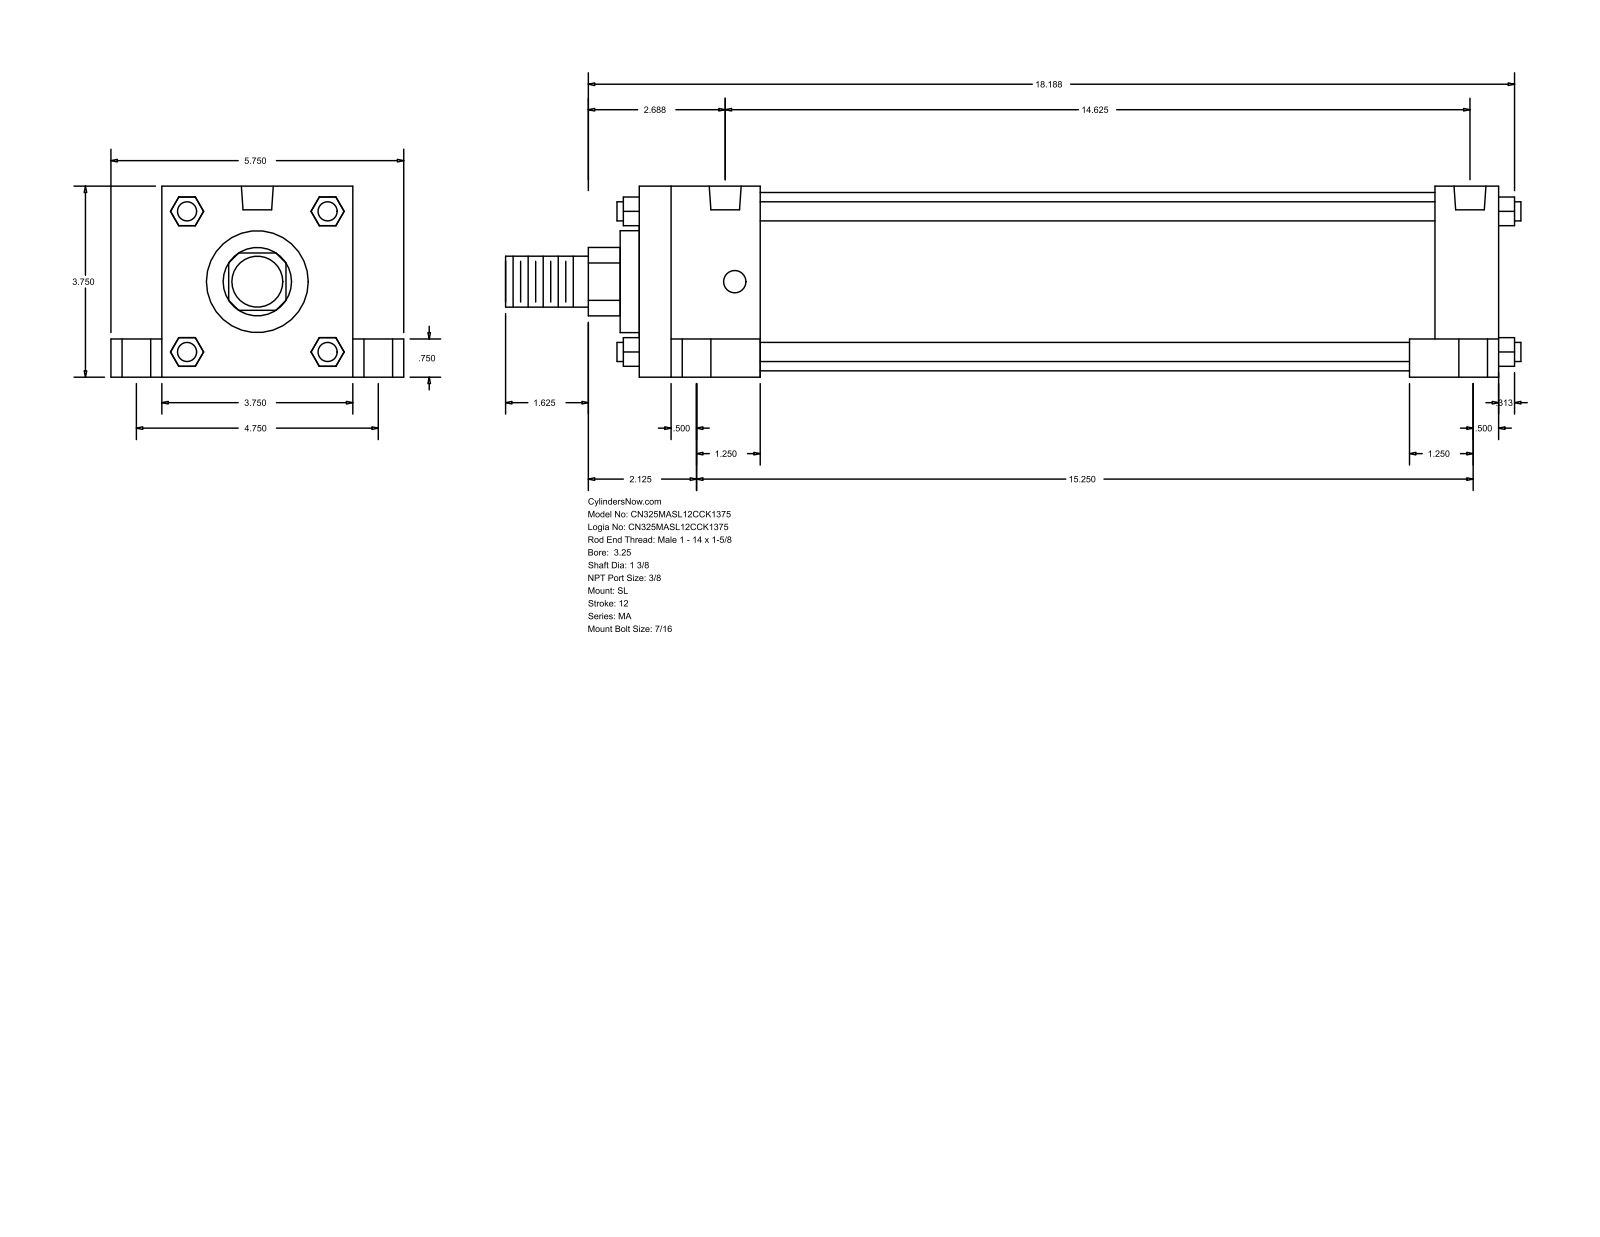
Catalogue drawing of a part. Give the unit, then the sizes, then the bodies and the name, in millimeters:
Units: millimetres
Overall size (bounding box): 506.41 × 146.05 × 95.25
Round holes (diameter × count): ⌀11.11 ×4, ⌀14.29 ×4, ⌀20.64 ×4, ⌀15.93 ×2
Round bosses / shafts (diameter × count): ⌀9.53 ×4, ⌀88.9 ×1, ⌀50.8 ×1, ⌀34.92 ×1, ⌀25.4 ×1
Partial cylindrical surfaces — rounded edges, fillets, slot ends (radius × count): R17.06 ×1
Main face-to-face distances: 95.24, 428.62, 336.55, 25.41, 120.65, 396.87, 31.75, 60.32, 368.3, 19.05
Hole centre spacings: 60.35, 60.66, 62, 63.27, 120.66, 361.95, 373.2, 377.91
Bodies: 0 solids, 148 faces (112 planar, 36 cylindrical, 0 other)
Part name (STEP PRODUCT): MA_SL__0325_1.375
STEP written by: GSSL Pune (CONFIG_CONTROL_DESIGN)
